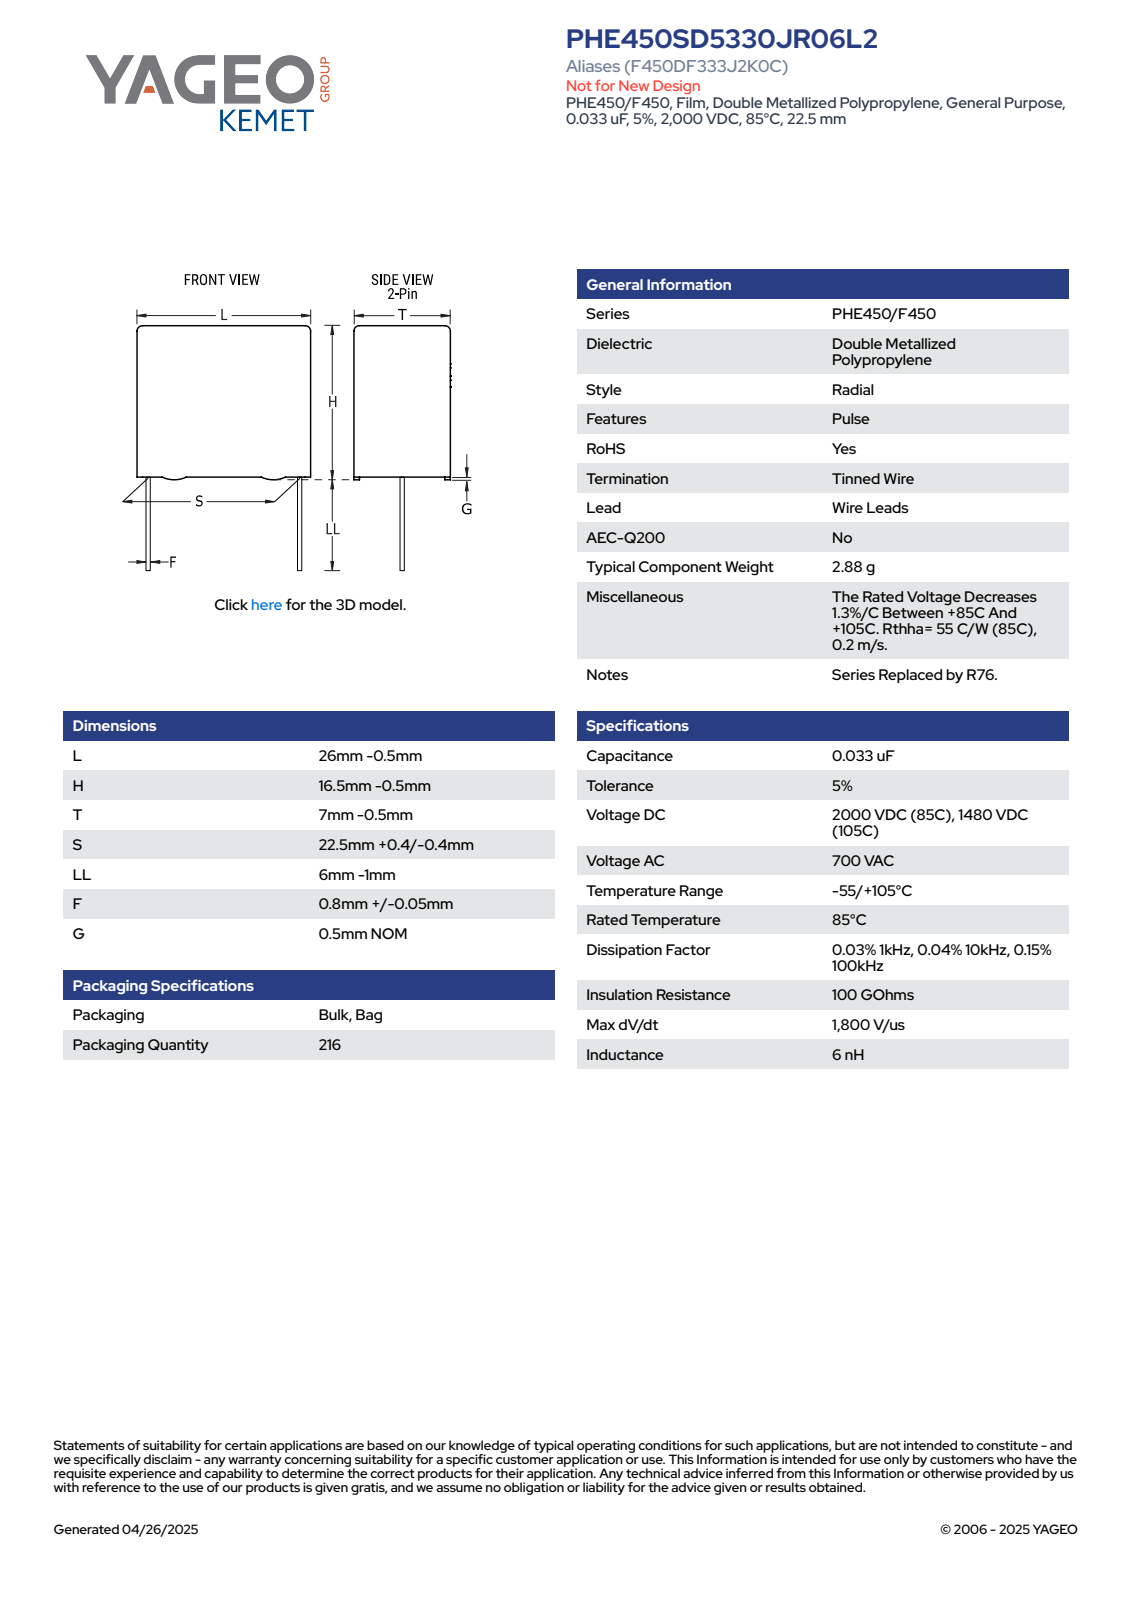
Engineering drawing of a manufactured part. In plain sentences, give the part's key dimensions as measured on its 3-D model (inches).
The part is named "CFR_RBG_26X16.5X7_L25.5H16T6.5S22.5LL5F0.85G0.5". Its 3-D file was written by "SolidWorks 2021 (AUTOMOTIVE_DESIGN)". It is 4 solids with 89 faces: 81 planar, 8 cylindrical and 0 other. Overall it measures 1.004 by 0.827 by 0.256 inches. Its volume is 0.157 cubic inches and its surface area 2.21 square inches. Round bosses or shafts: 2 of diameter 0.033. Partial cylindrical surfaces (rounded edges, fillets, slot ends): 4 of radius 0.02. The main face-to-face distances are 0.256, 0.61, 1.004, 0.015, 0.241, 0.02, 0.63, 0.227, 0.197, 0.217.
